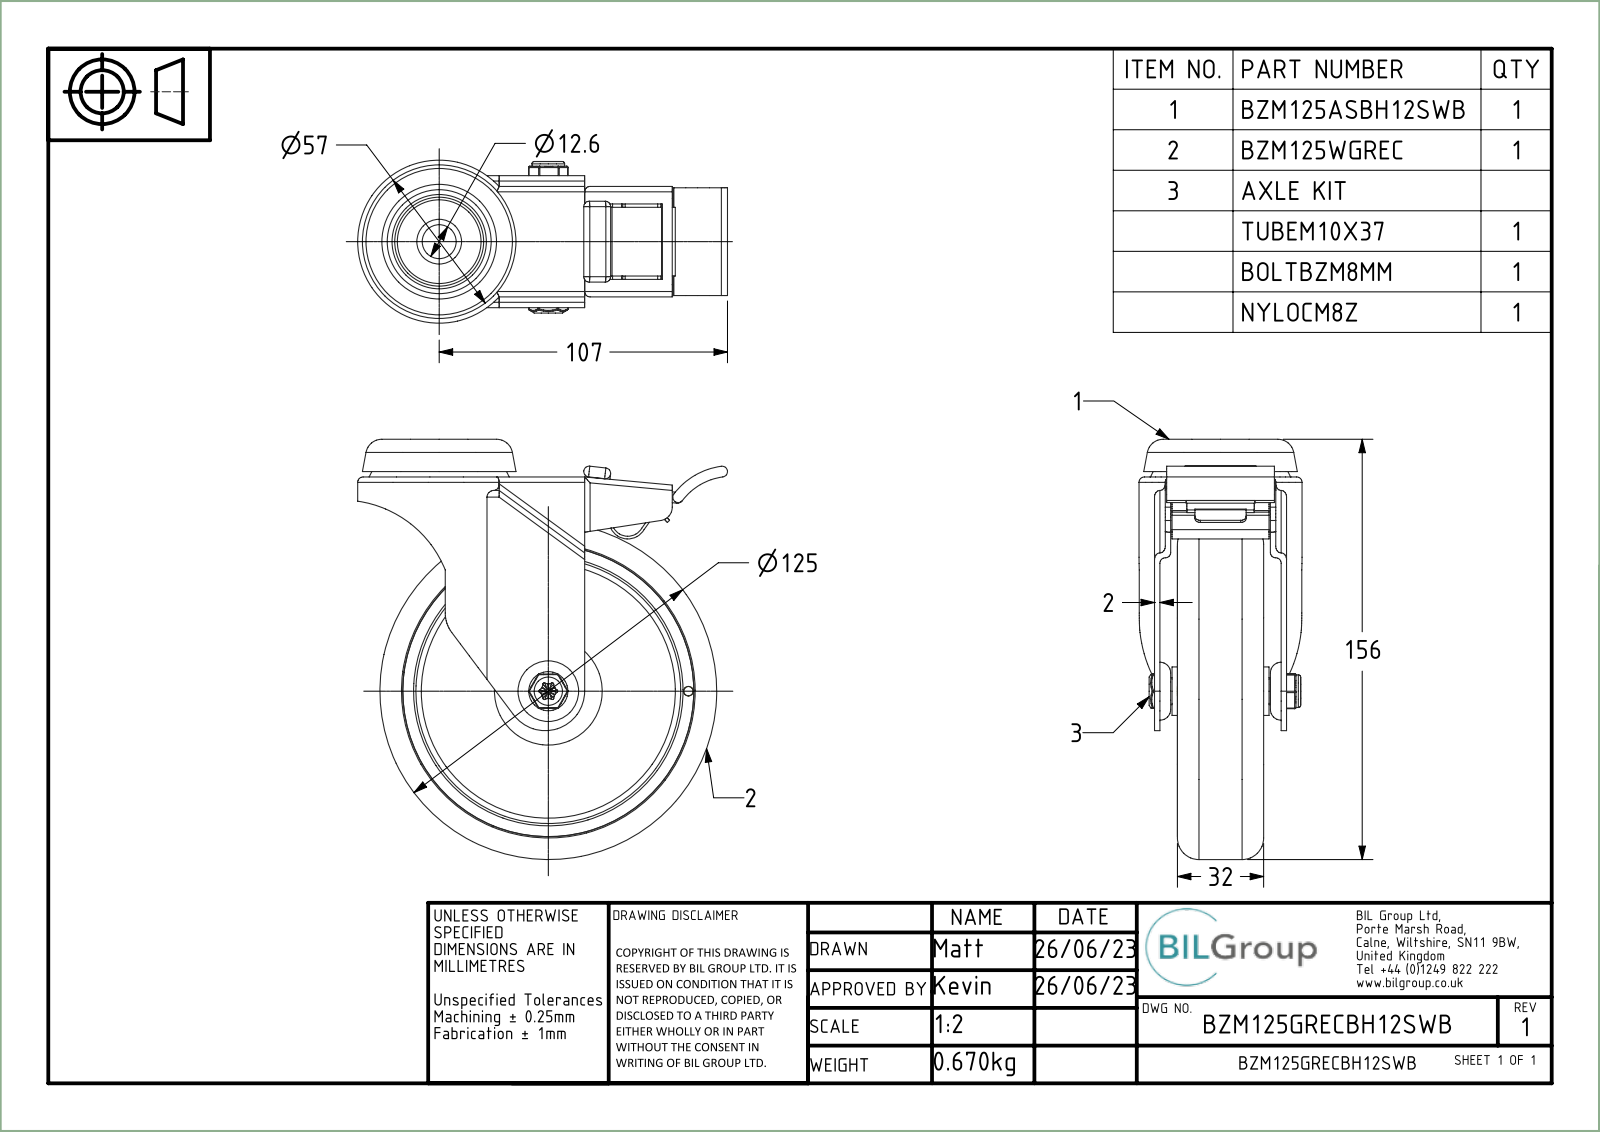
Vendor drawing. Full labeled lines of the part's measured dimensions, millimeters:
Part name (STEP PRODUCT): BZM125ASBH12SWB; ZINC PLATED PRESSED STEEL HEAD; ZINC PLATED PRESSED STEEL FORKS; ZINC PLATED PRESSED STEEL BRAKE (+8 more)
STEP written by: Spatial InterOp 3D (CONFIG_CONTROL_DESIGN)
Units: millimetres
Bodies: 12 solids, 646 faces (211 planar, 289 cylindrical, 146 other)
Overall size (bounding box): 156 × 137.25 × 60.5
Volume: 240 198 mm³ · Surface area: 125 654 mm²
Round holes (diameter × count): ⌀3.5 ×1, ⌀8 ×1, ⌀8.2 ×1, ⌀8.5 ×1, ⌀8.6 ×1, ⌀10.1 ×1, ⌀10.3 ×1, ⌀12.6 ×1, ⌀46 ×1, ⌀108 ×1
Round bosses / shafts (diameter × count): ⌀125 ×1, ⌀48 ×1, ⌀30 ×1, ⌀18 ×1, ⌀12.1 ×1, ⌀10 ×1, ⌀6 ×1
Partial cylindrical surfaces — rounded edges, fillets, slot ends (radius × count): R2 ×40, R0.5 ×30, R1 ×7, R6 ×4, R1.5 ×2, R3 ×2, R5 ×2, R0.88 ×1
Main face-to-face distances: 4, 2, 20.5, 22.5, 43, 6, 26.5, 41, 14, 18
Hole centre spacings: 52
